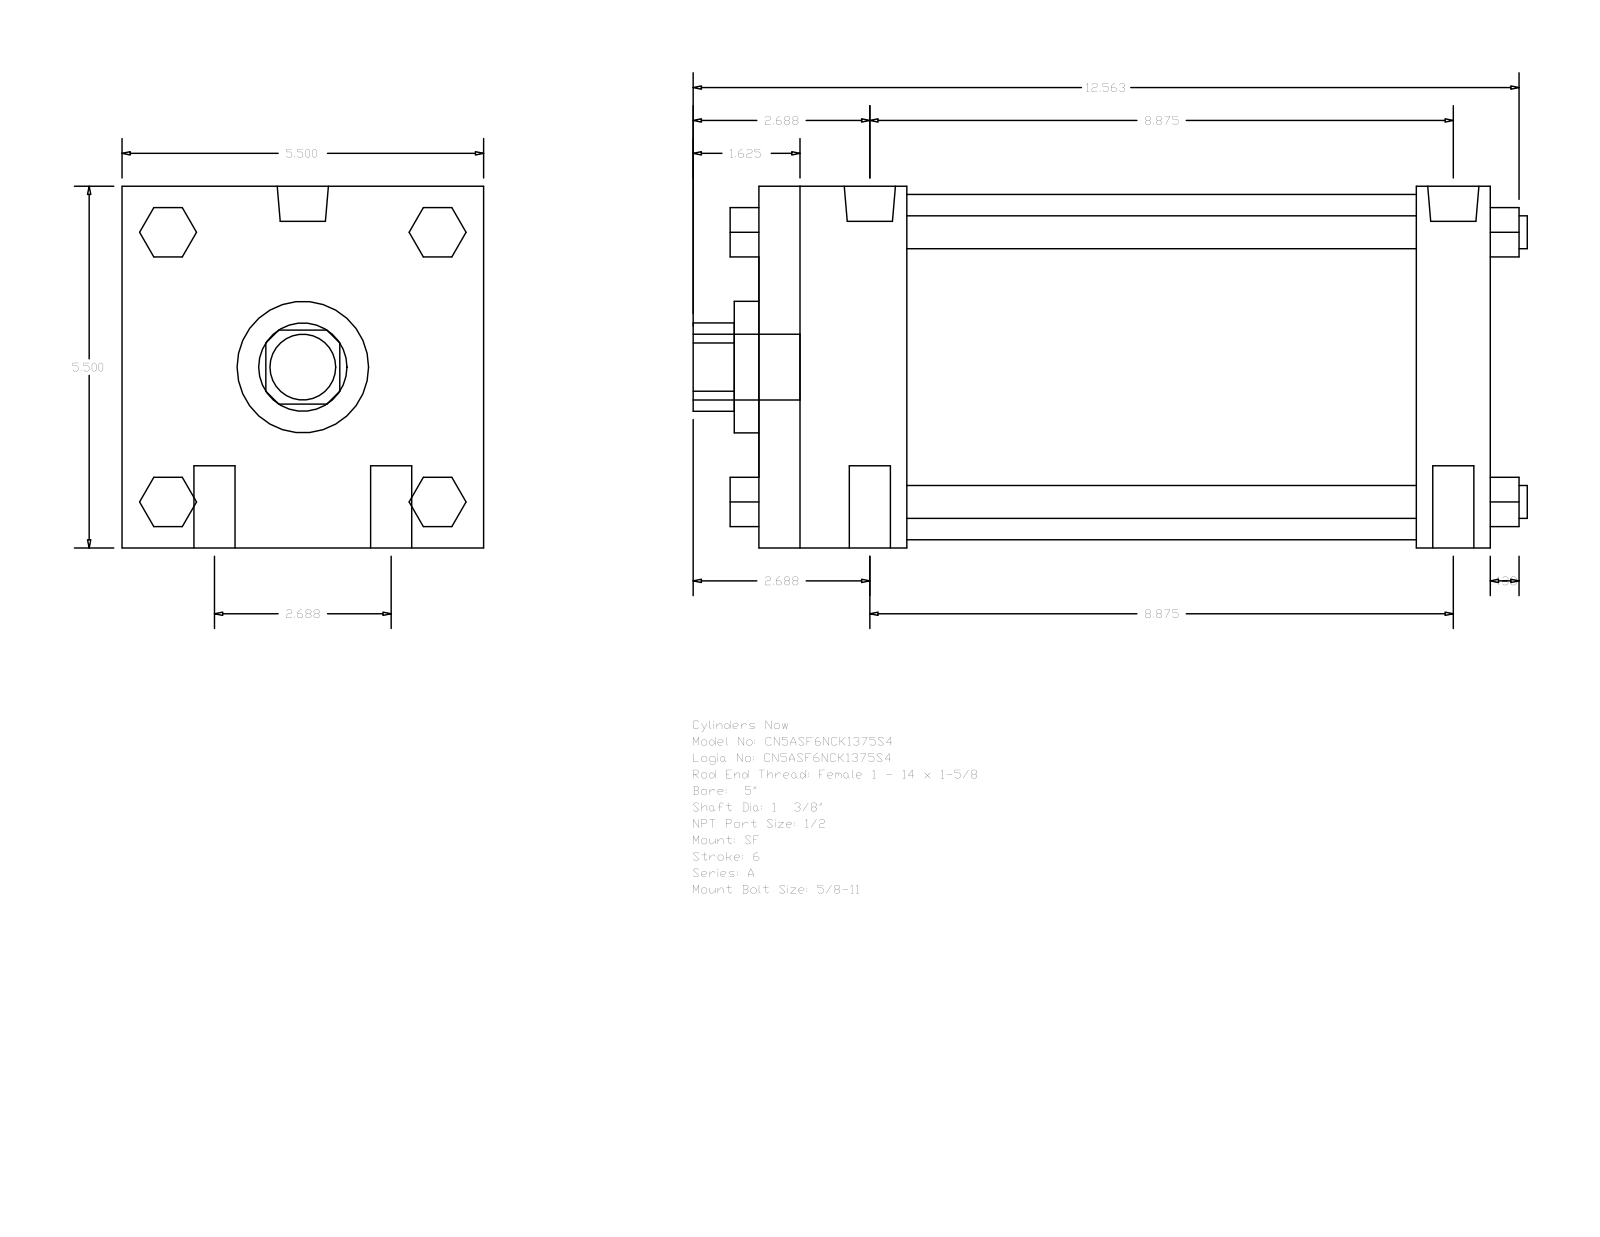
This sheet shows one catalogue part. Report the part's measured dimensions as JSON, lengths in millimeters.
{"part_name": "A_SF__0500_1.375", "step_written_by": "GSSL Pune (CONFIG_CONTROL_DESIGN)", "units": "millimeters", "bodies": {"solids": 0, "faces": 124, "planar": 94, "cylindrical": 30, "other": 0}, "overall_size": [322.26, 139.7, 139.7], "round_holes": [[34.92, 1], [50.8, 1], [133.35, 1]], "round_bosses_or_shafts": [[15.88, 4], [12.7, 4], [19.77, 2], [8.73, 2], [25.4, 1]], "partial_cylinders_radius": [[17.06, 1]], "face_to_face_distances": [139.7, 282.58, 28.58, 57.15, 254, 196.85, 225.43, 19.05, 52.07, 90.18]}
